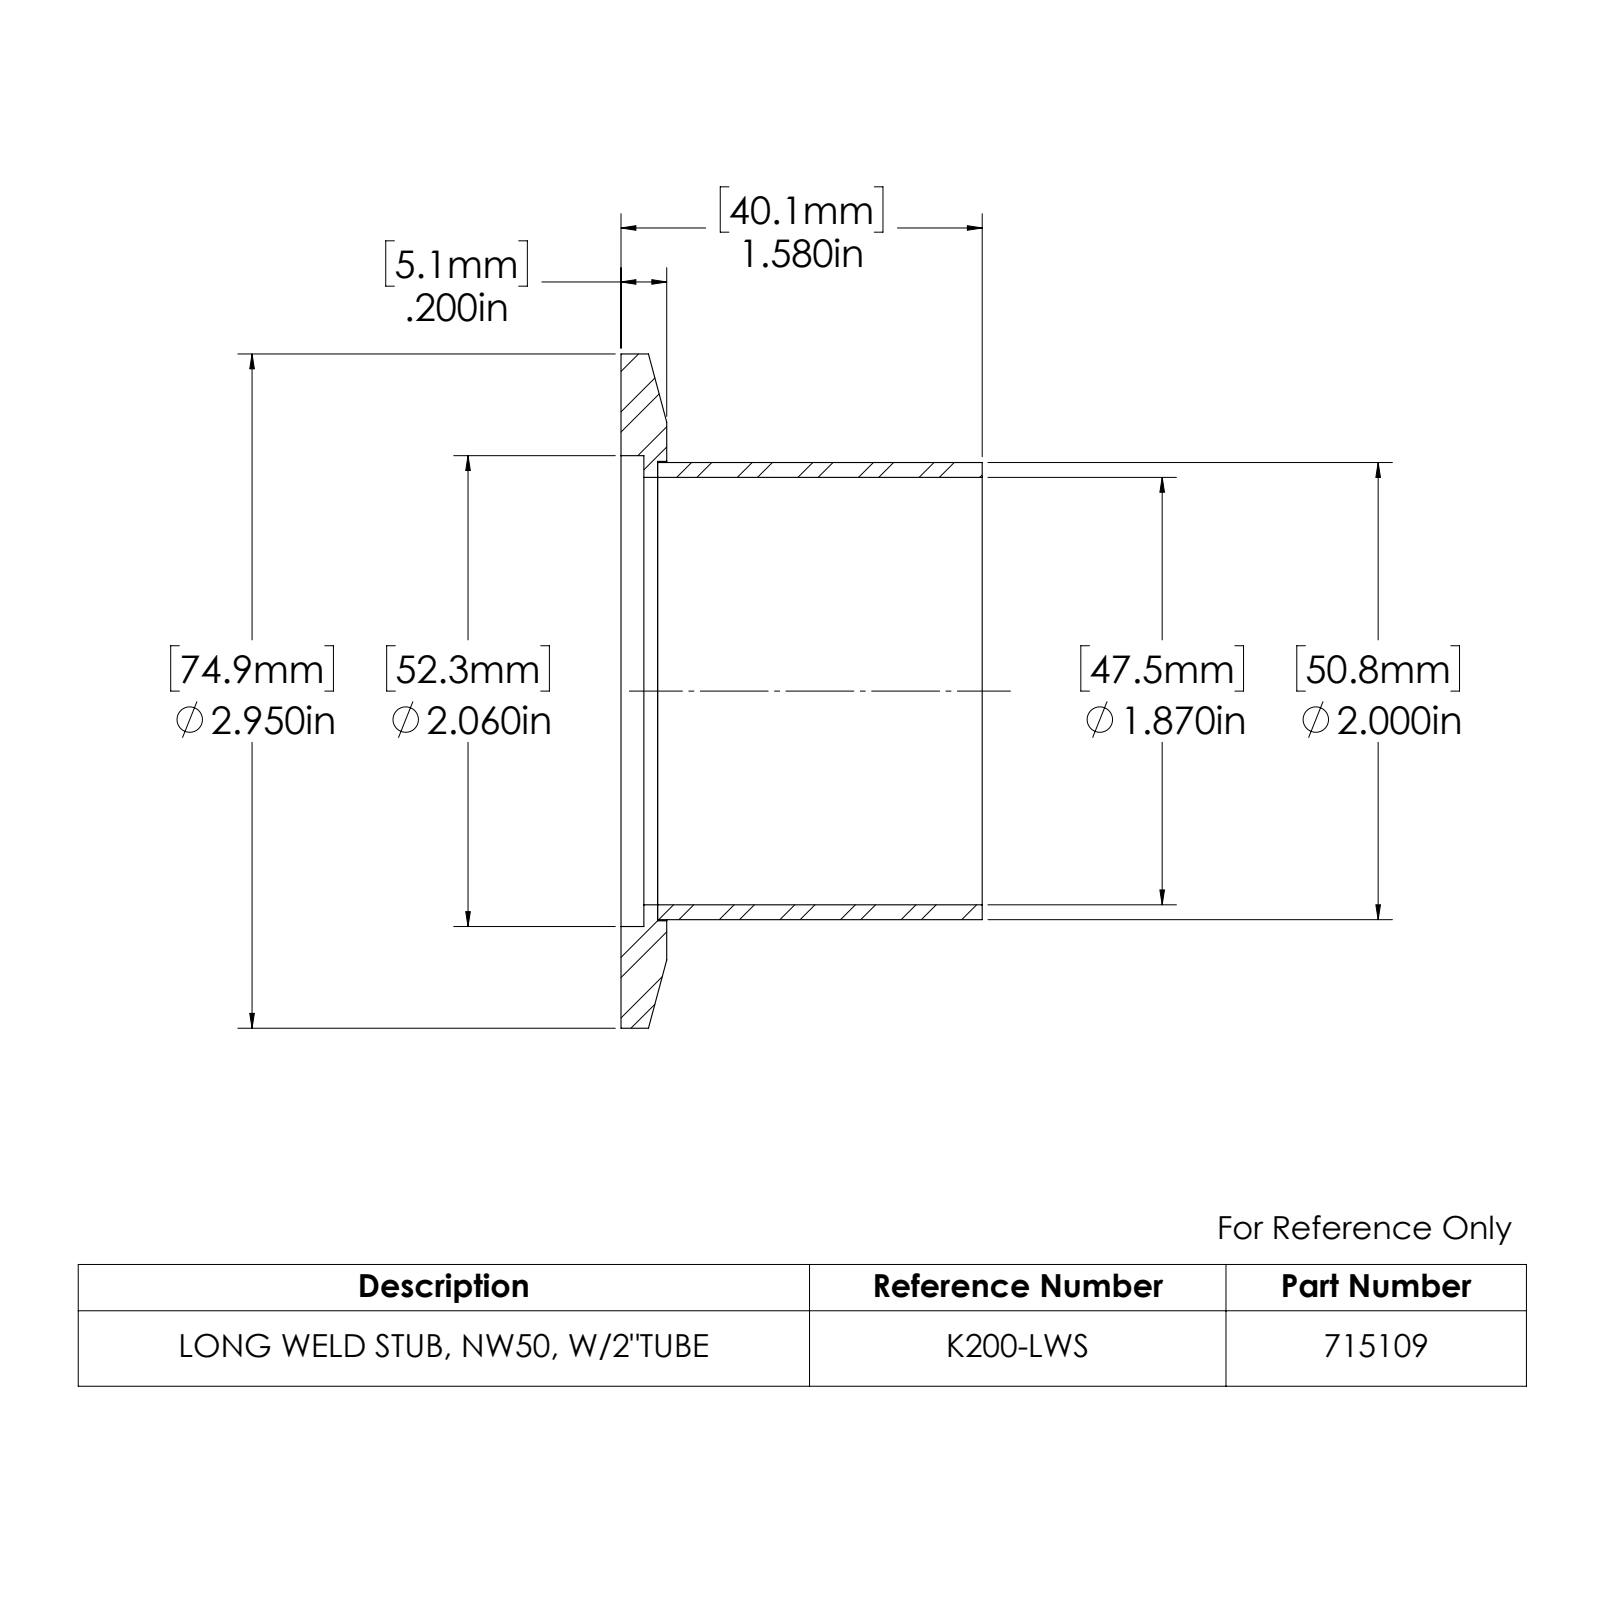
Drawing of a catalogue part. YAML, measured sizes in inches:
part_name: "713022; 715109-REV.B; 971504-REV.B"
step_written_by: "SolidWorks 2022 (AUTOMOTIVE_DESIGN)"
units: inches
bodies: {solids: 2, faces: 20, planar: 6, cylindrical: 12, other: 2}
overall_size: [2.95, 2.95, 1.63]
volume: 1.2
surface_area: 28.68
round_holes:
  - {diameter: 1.87, count: 1}
  - {diameter: 2.01, count: 1}
  - {diameter: 2.06, count: 1}
round_bosses_or_shafts:
  - {diameter: 2.95, count: 1}
  - {diameter: 2, count: 1}
face_to_face_distances: [0.2, 0.1, 0.16, 0.06, 0.04, 0.209, 1.63, 0.109, 1.53, 0.05]
